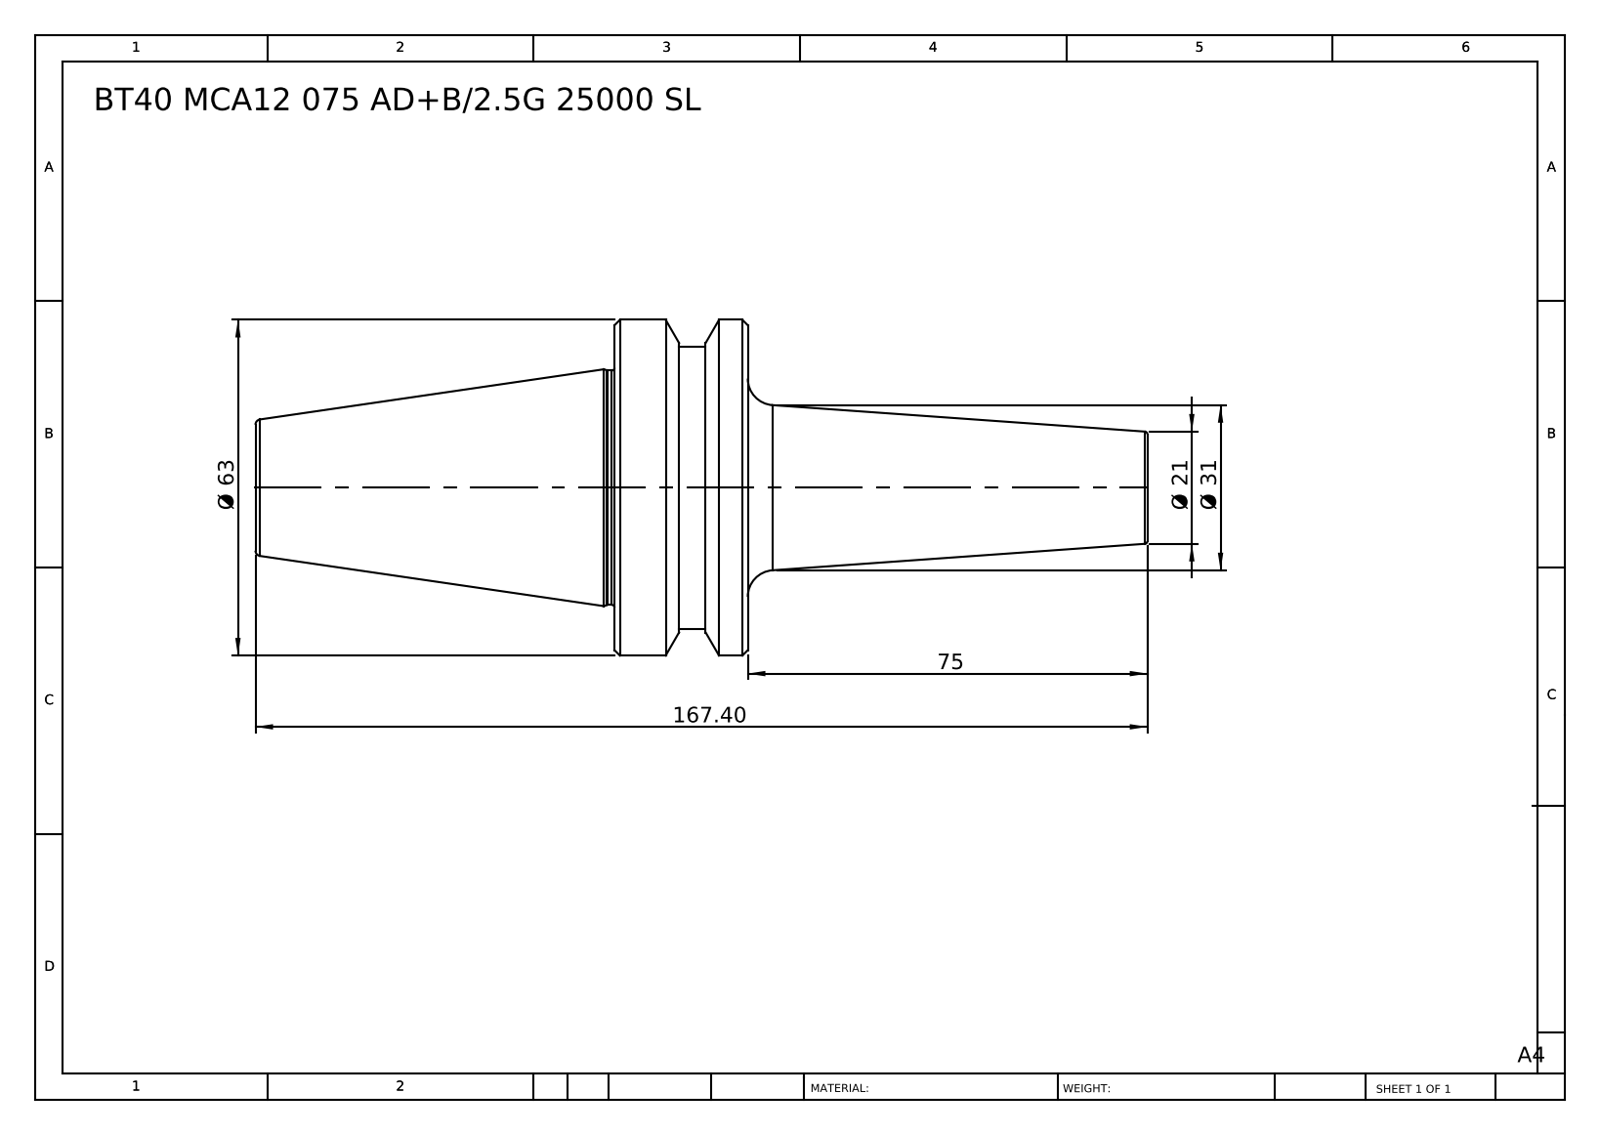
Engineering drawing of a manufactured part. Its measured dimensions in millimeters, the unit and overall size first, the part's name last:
Units: millimetres
Overall size (bounding box): 167.4 × 63 × 63
Round bosses / shafts (diameter × count): ⌀63 ×1, ⌀53 ×1, ⌀44 ×1
Main face-to-face distances: 25, 92.4, 67.4, 75, 100, 167.4, 87.9, 12.9, 12.1, 79.5
Volume: 180 218 mm³ · Surface area: 23 929 mm²
Bodies: 1 solid, 38 faces (6 planar, 8 cylindrical, 24 other)
Part name (STEP PRODUCT): BT40 MCA12 075 AD+B-2.5G 25000 SL
STEP written by: SolidWorks 2014 (CONFIG_CONTROL_DESIGN)
